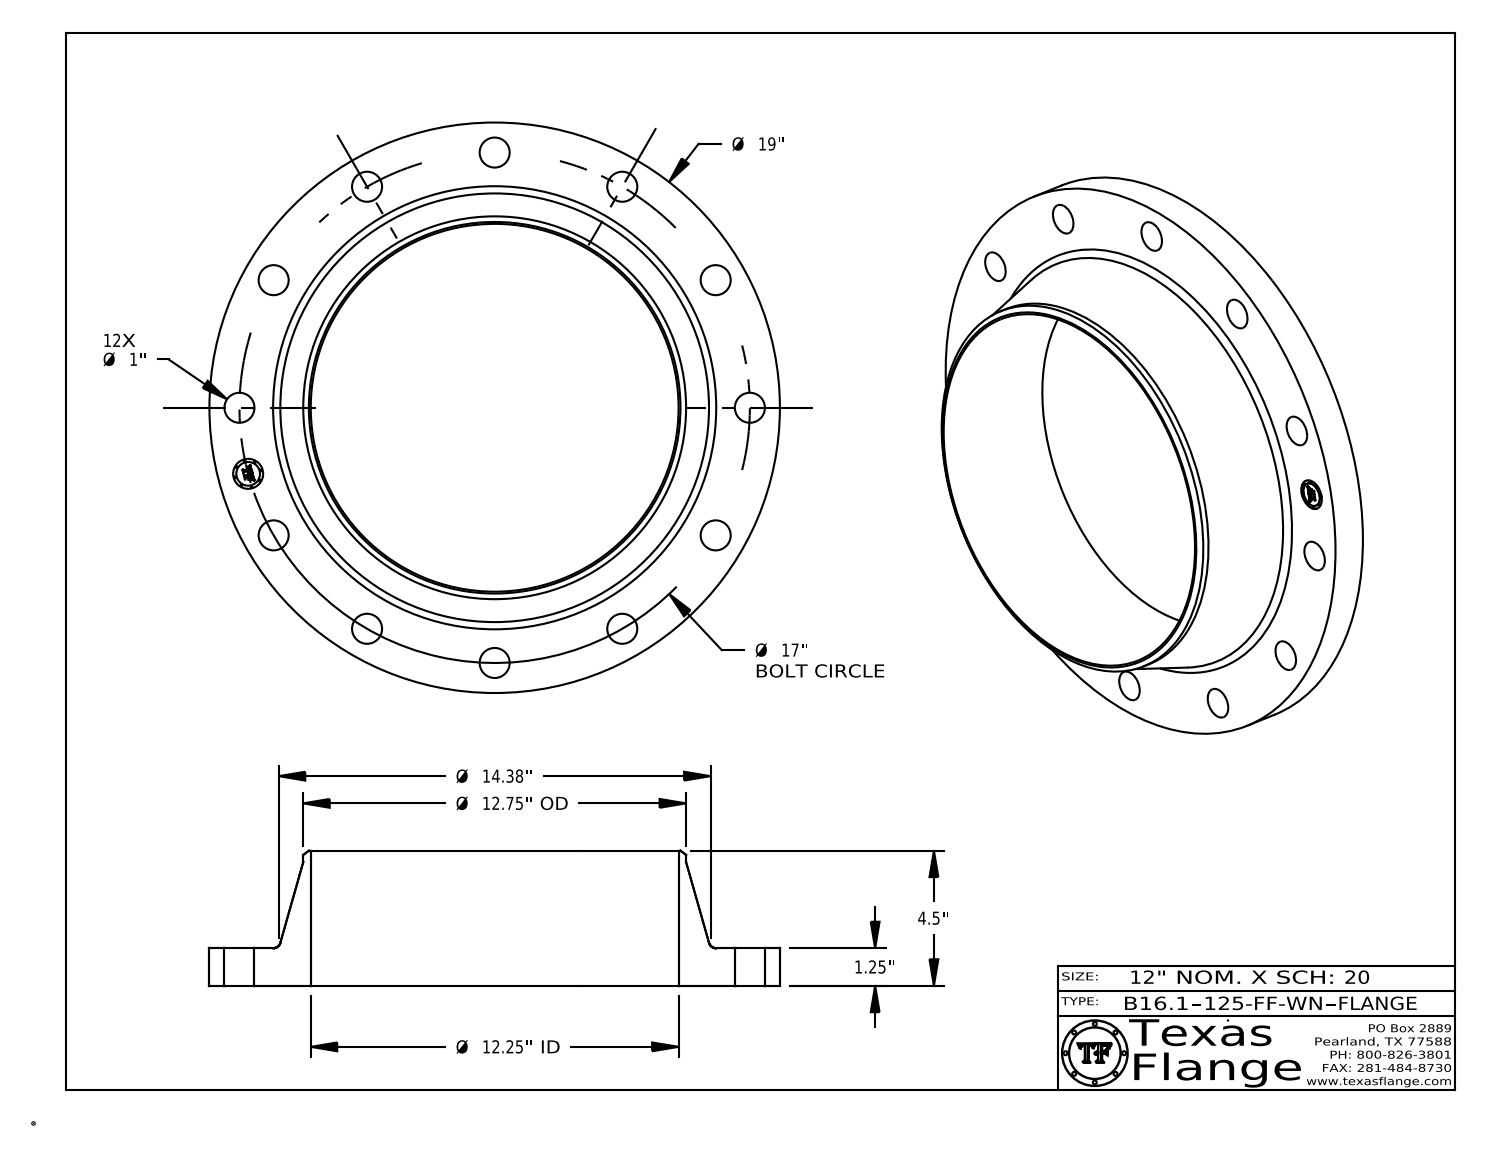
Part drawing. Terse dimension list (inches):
name: B16.1, Class 125-FF-WN
written by: CATIA V5 STEP AP214 (AUTOMOTIVE_DESIGN)
unit: in
bodies: 1 solid, 424 faces (368 planar, 50 cylindrical, 6 other)
size: 19 × 19 × 4.5
volume: 275.8 in³; area: 709 in²
holes: 13× ⌀1, 1× ⌀12.25
bosses: 8× ⌀0.061, 1× ⌀19, 1× ⌀12.75, 1× ⌀0.788
face distances: 1.25, 4.5, 3.25, 0.015, 1.235, 3.265, 0.298, 0.292, 0.054, 0.193
hole spacings: 8.5, 16.42, 4.4, 12.02, 14.722, 4.4, 12.021, 14.722
